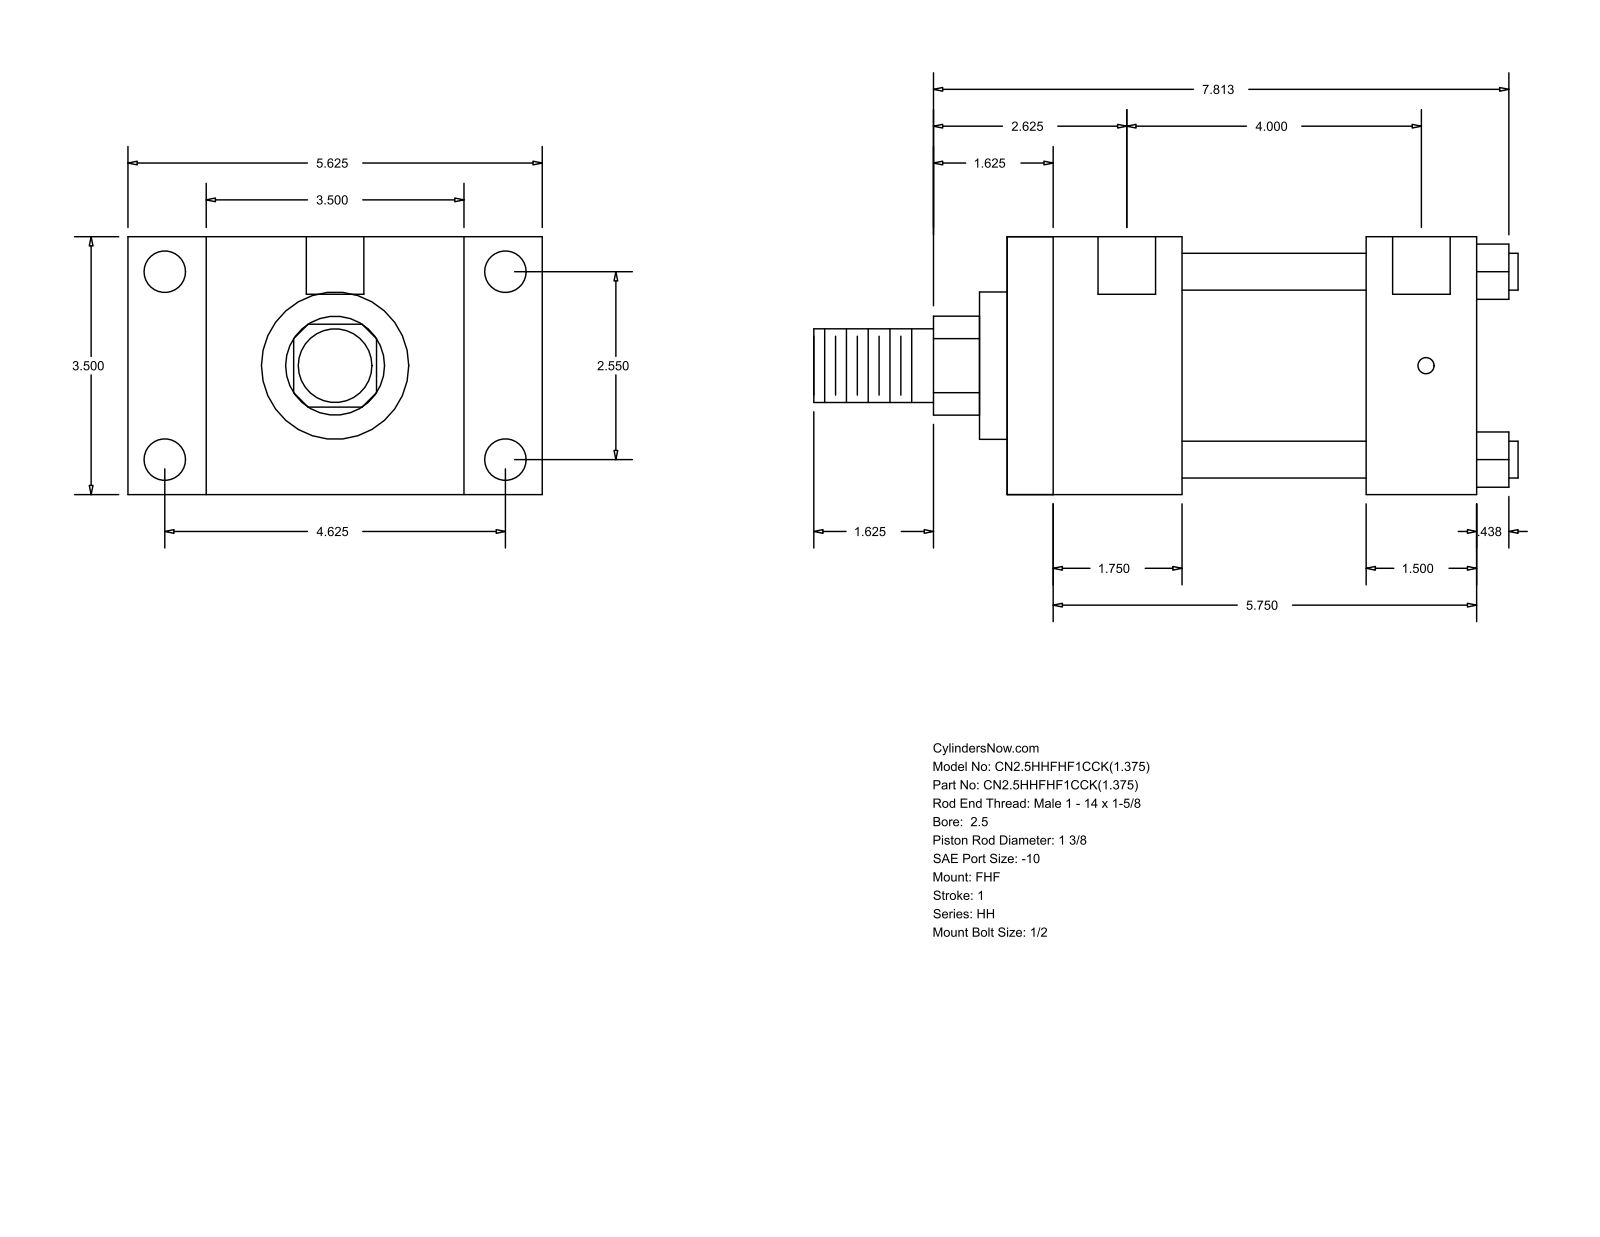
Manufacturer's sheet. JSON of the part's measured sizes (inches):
{"part_name": "HH_FHF__0250_1.375", "step_written_by": "GSSL Pune (CONFIG_CONTROL_DESIGN)", "units": "inches", "bodies": {"solids": 0, "faces": 88, "planar": 60, "cylindrical": 28, "other": 0}, "overall_size": [9.563, 5.625, 3.5], "round_holes": [[0.219, 4], [0.563, 4], [0.781, 2]], "round_bosses_or_shafts": [[0.5, 4], [2.875, 1], [2, 1], [1.375, 1], [1, 1]], "partial_cylinders_radius": [[0.672, 1]], "face_to_face_distances": [3.5, 2.375, 4.563, 1.063, 6.375, 4, 5.625, 4.875, 2.5, 1.5], "hole_center_spacings": [0.062, 2.55, 4.063, 4.125, 4.625, 5.281, 4]}
